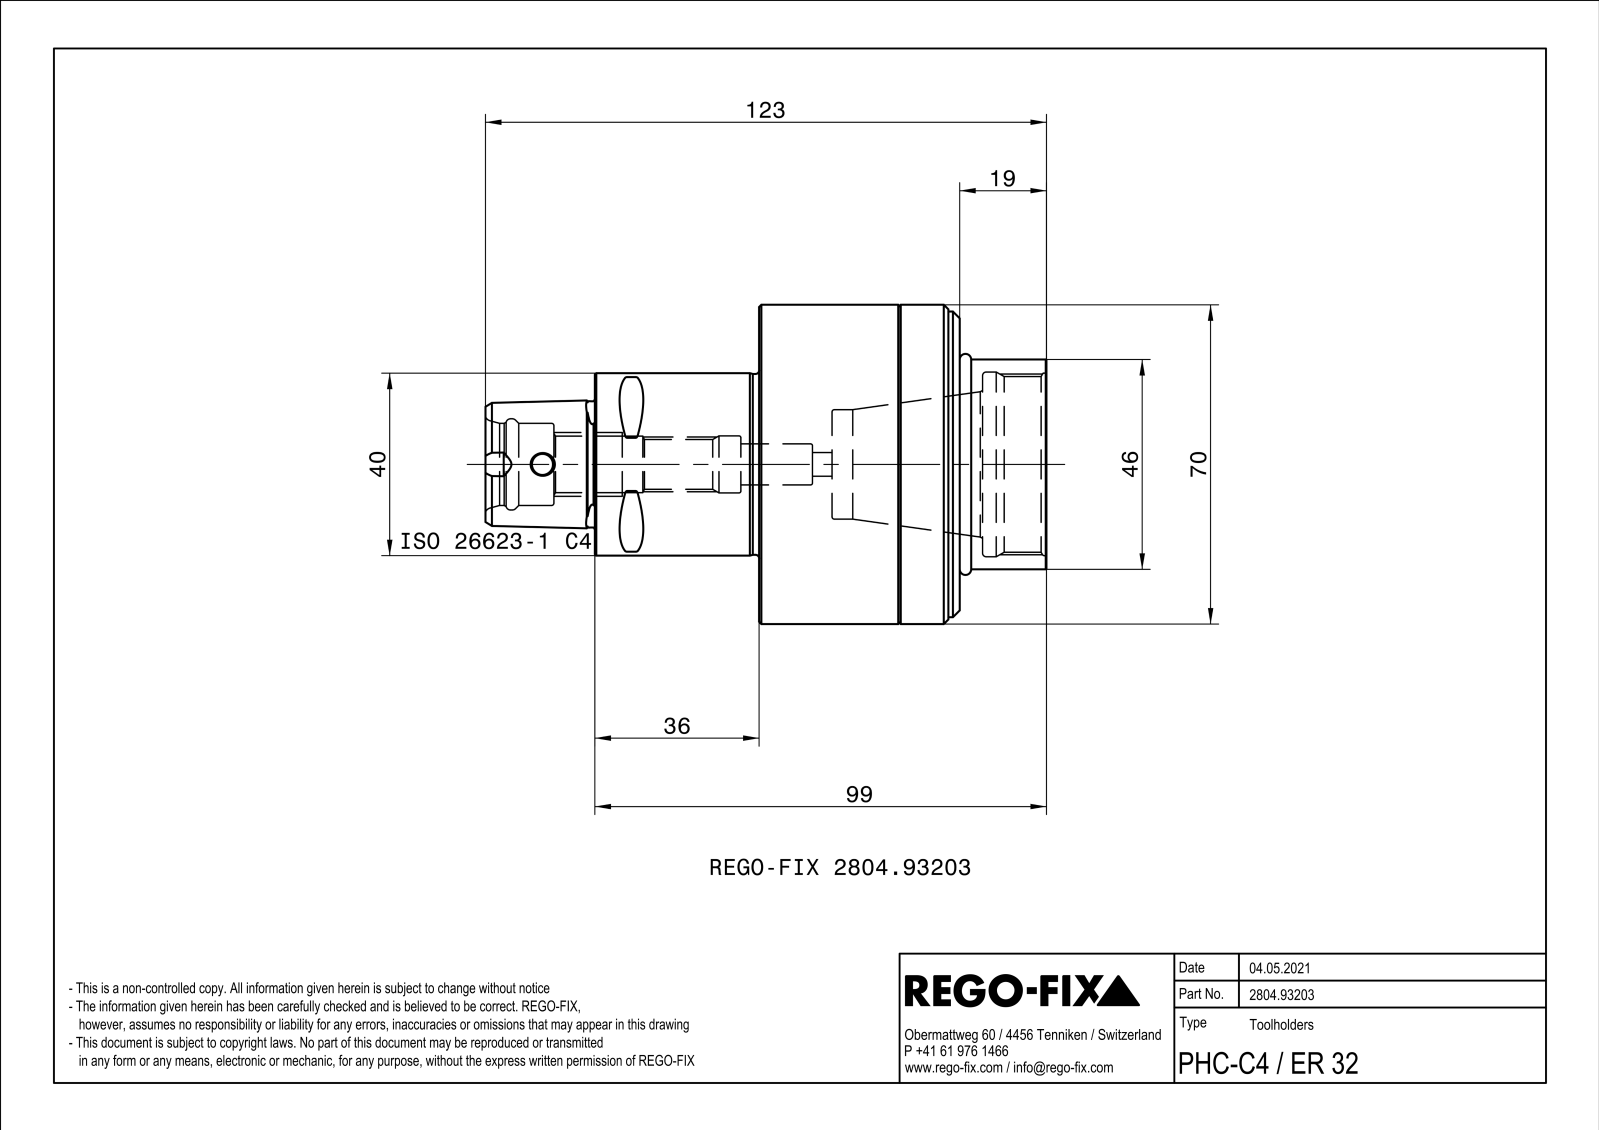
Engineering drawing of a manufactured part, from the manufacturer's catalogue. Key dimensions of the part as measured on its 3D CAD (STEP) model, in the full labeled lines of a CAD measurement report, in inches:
Part name (STEP PRODUCT): NOCUT
STEP written by: SIEMENS PLM Software Solid Edge ST10 (AUTOMOTIVE_DESIGN)
Units: inches
Bodies: 1 solid, 215 faces (43 planar, 52 cylindrical, 120 other)
Overall size (bounding box): 4.843 × 2.756 × 2.756
Volume: 10.7 in³ · Surface area: 89.14 in²
Round holes (diameter × count): ⌀0.197 ×4, ⌀0.083 ×1, ⌀0.126 ×1, ⌀0.157 ×1, ⌀0.181 ×1, ⌀0.205 ×1, ⌀0.291 ×1, ⌀0.354 ×1, ⌀0.43 ×1, ⌀0.487 ×1, ⌀0.492 ×1, ⌀0.709 ×1
Round bosses / shafts (diameter × count): ⌀2.756 ×1, ⌀2.638 ×1, ⌀2.362 ×1, ⌀2.303 ×1, ⌀2.299 ×1, ⌀2.126 ×1, ⌀2.102 ×1, ⌀1.575 ×1
Partial cylindrical surfaces — rounded edges, fillets, slot ends (radius × count): R0.02 ×8, R0.118 ×1
Main face-to-face distances: 0.236, 0.472, 0.224, 0.484, 0.248, 0.709, 1.26, 1.024, 1.732, 1.508
Hole centre spacings: 0.945, 1.336, 1.89, 0.925, 1.094, 1.268, 2.193, 2.362
